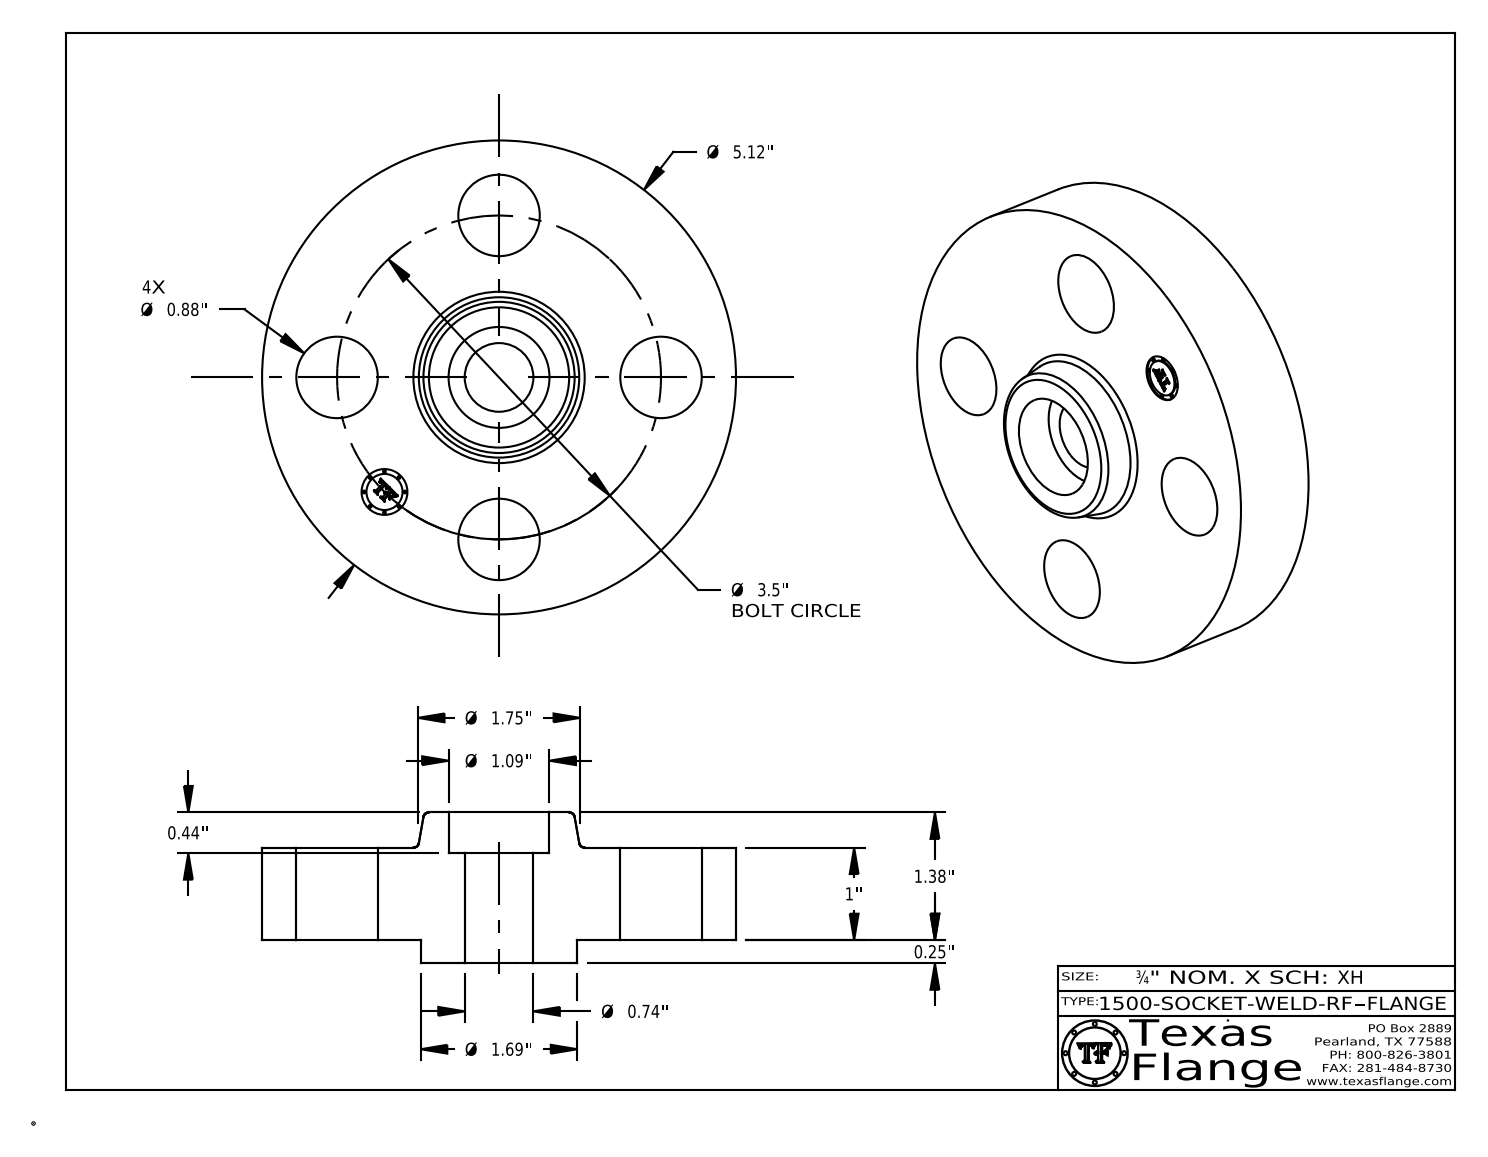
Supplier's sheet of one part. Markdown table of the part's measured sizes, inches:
| quantity | value |
| --- | --- |
| part name | 1500-SOCKET-WELD-RF |
| STEP written by | CATIA V5 STEP AP214 (AUTOMOTIVE_DESIGN) |
| units | inches |
| bodies | 1 solid, 412 faces (370 planar, 36 cylindrical, 6 other) |
| overall size | 5.12 × 5.12 × 1.63 |
| volume | 18.64 in³ |
| surface area | 69.8 in² |
| round holes (diameter × count) | 0.88 × 4, 0.495 × 1, 0.742 × 1, 1.09 × 1 |
| round bosses / shafts (diameter × count) | 0.03 × 8, 5.12 × 1, 1.69 × 1, 0.39 × 1 |
| main face-to-face distances | 1, 0.25, 1.25, 1.63, 1.38, 0.38, 0.06, 1.19, 0.94, 0.44 |
| hole center spacings | 1.75, 2.475, 1.339, 3.233, 3.5 |
